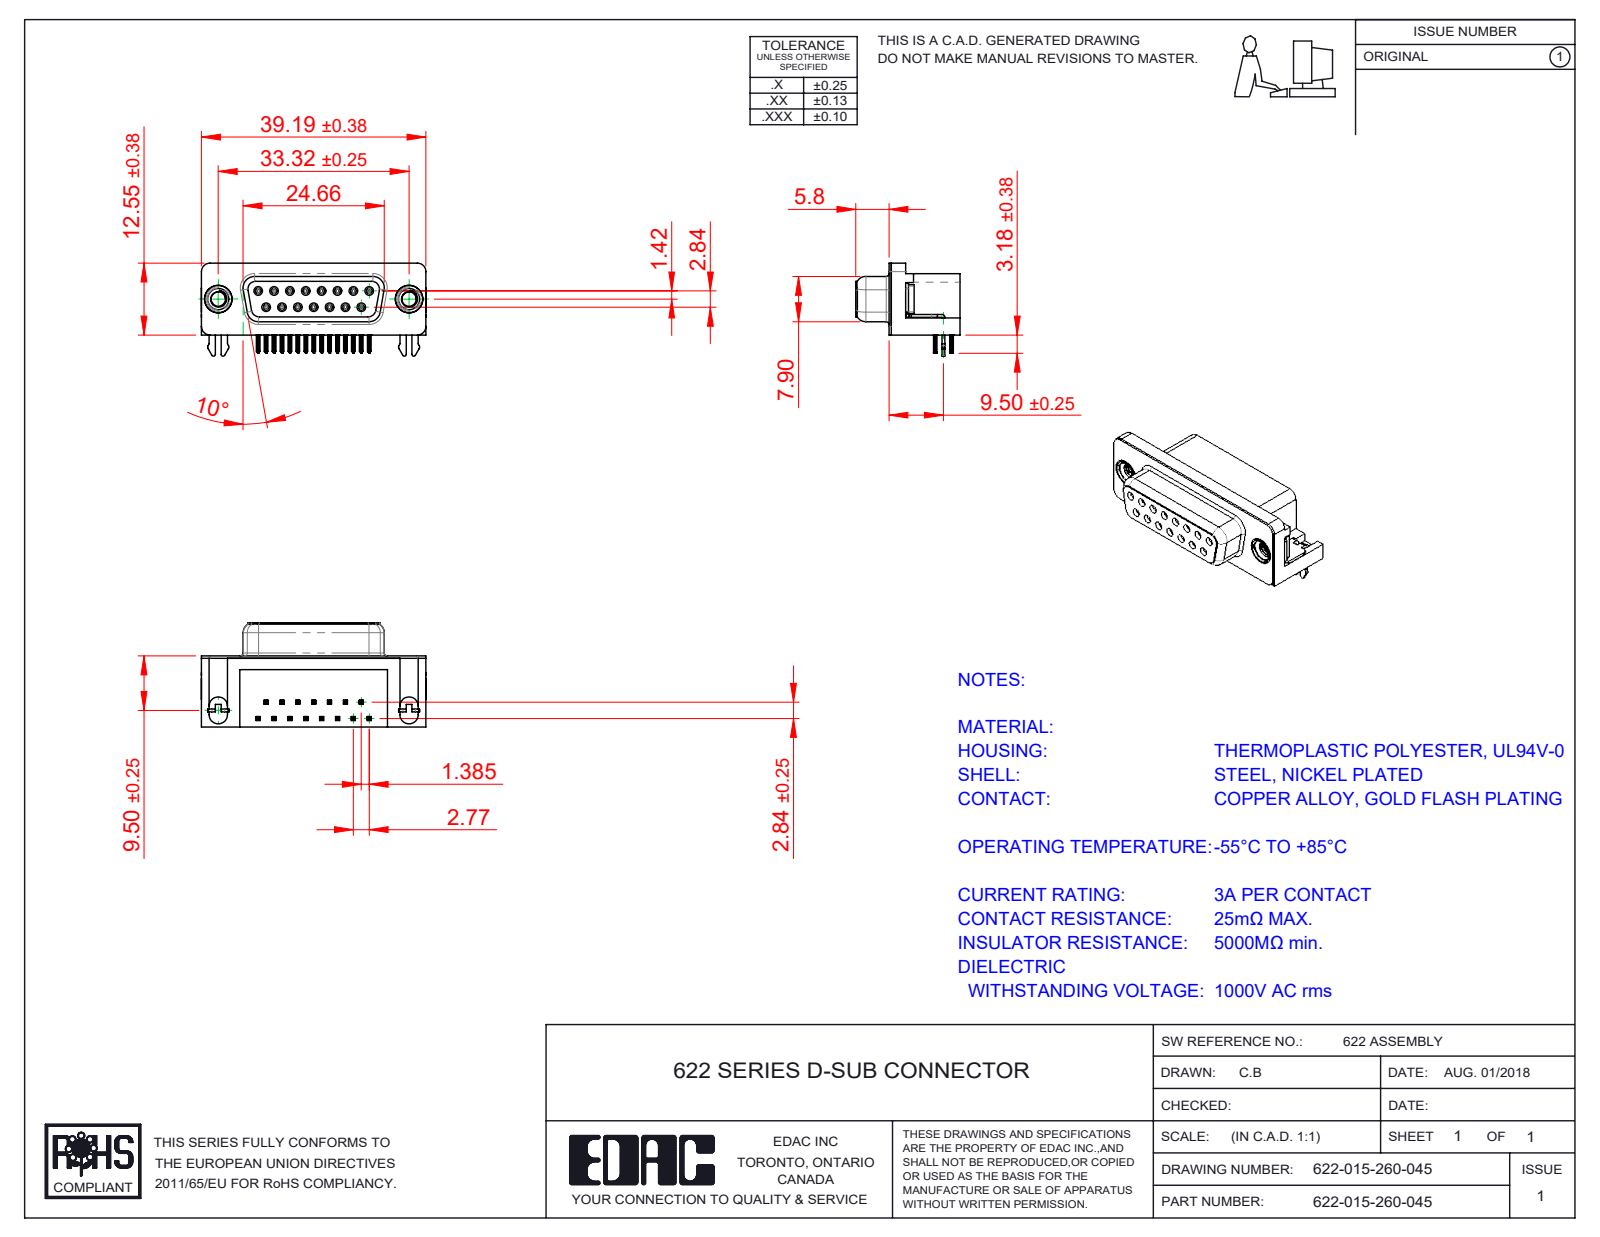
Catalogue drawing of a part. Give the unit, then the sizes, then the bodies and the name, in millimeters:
Units: millimetres
Overall size (bounding box): 39.22 × 18.2 × 16.25
Round holes (diameter × count): ⌀0.8 ×15, ⌀0.9 ×15, ⌀2 ×2, ⌀2.5 ×2, ⌀4 ×2, ⌀4.8 ×2, ⌀5 ×2
Round bosses / shafts (diameter × count): ⌀1.2 ×15, ⌀4.9 ×2, ⌀4.75 ×2, ⌀3.9 ×2, ⌀3 ×2
Partial cylindrical surfaces — rounded edges, fillets, slot ends (radius × count): R0.1 ×120, R0.15 ×60, R0.35 ×30, R1 ×18, R0.34 ×15, R0.25 ×12, R1.35 ×8, R1.5 ×8
Main face-to-face distances: 0.4, 12, 6.2, 12.4, 10.35, 2.9, 6.65, 0.85, 0.35, 5.8
Hole centre spacings: 3.16, 2.77, 5.54, 8.31, 11.08, 5.03, 5.04, 7.48
Volume: 5 192 mm³ · Surface area: 6 794 mm²
Bodies: 21 solids, 2547 faces (1116 planar, 615 cylindrical, 816 other)
Part name (STEP PRODUCT): 622 Socket Bottom; 622 M3 Threaded Rivet; 622 Housing_15 Socket; 622-015-260-045 (+3 more)
STEP written by: SolidWorks 2016 (CONFIG_CONTROL_DESIGN)
